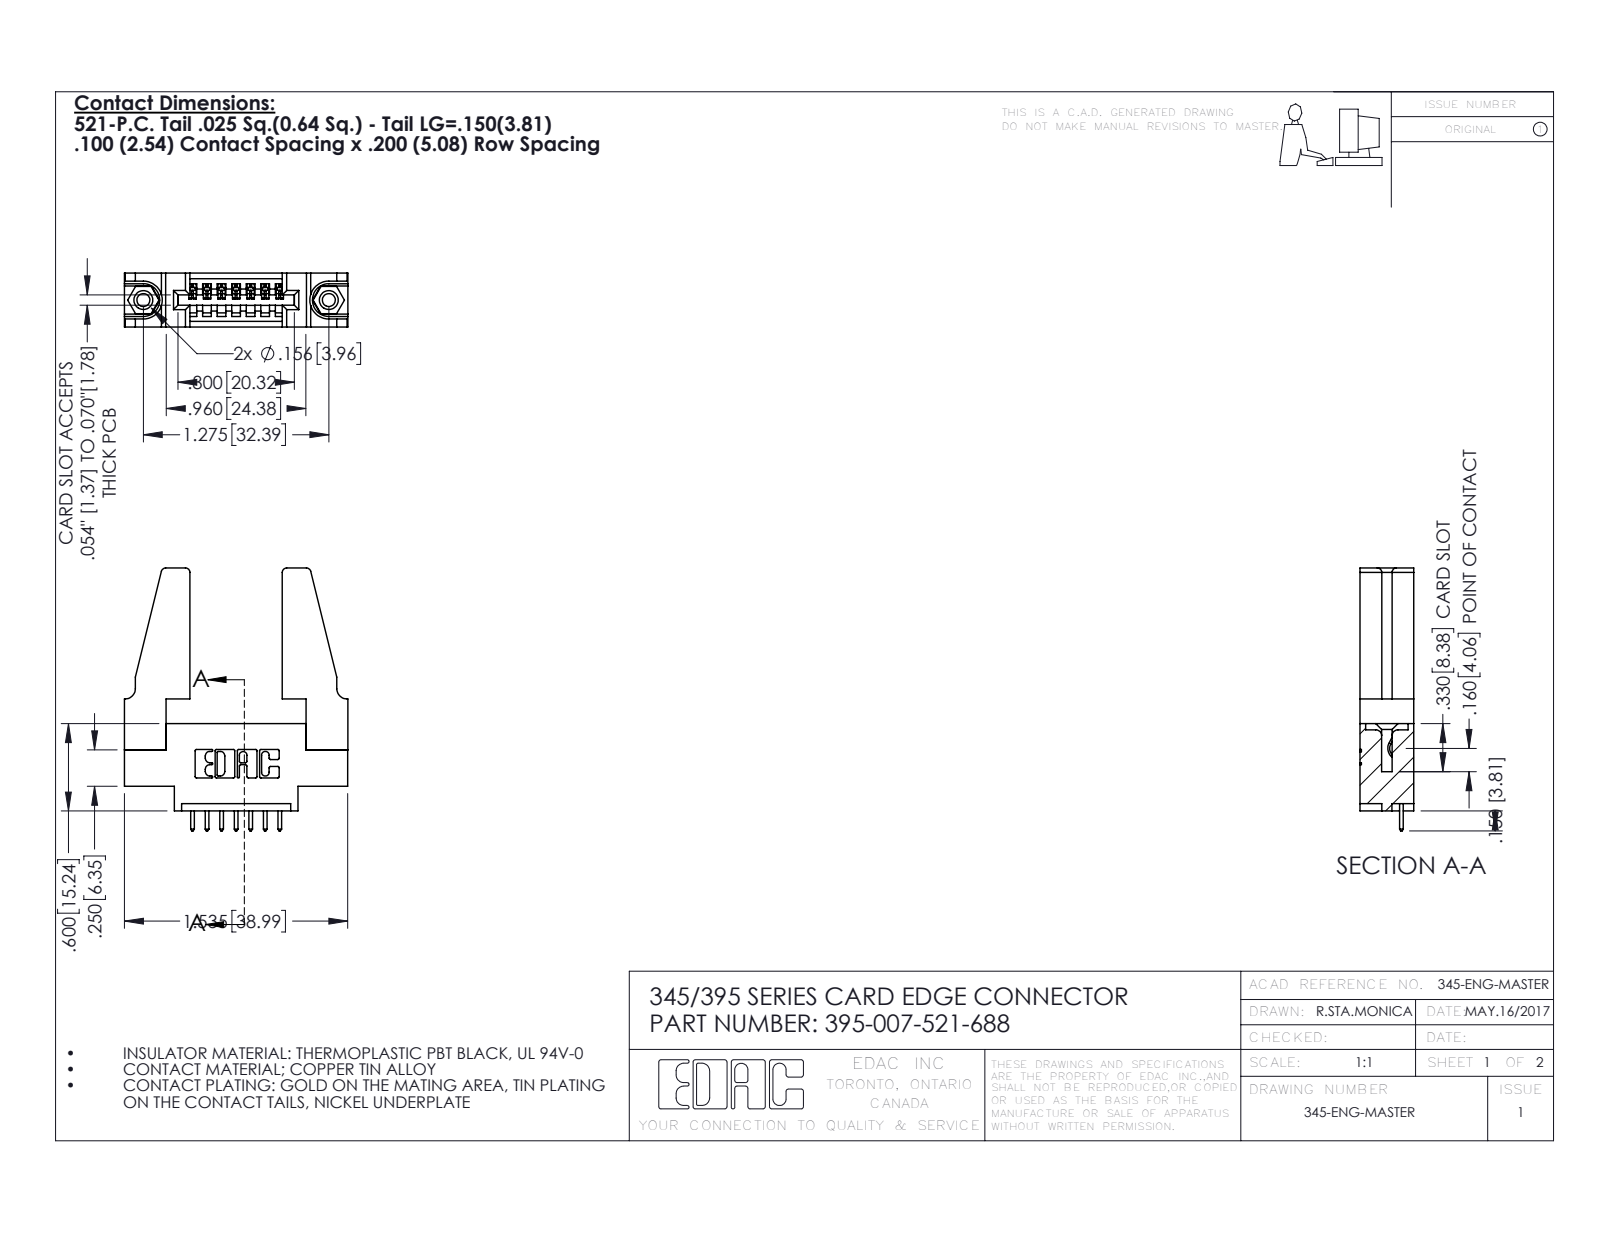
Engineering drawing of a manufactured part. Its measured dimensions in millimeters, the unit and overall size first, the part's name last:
Units: millimetres
Overall size (bounding box): 45.9 × 39 × 9.4
Round holes (diameter × count): ⌀2.3 ×2, ⌀3.2 ×2, ⌀4 ×2, ⌀1.6 ×1
Round bosses / shafts (diameter × count): ⌀3.9 ×2
Partial cylindrical surfaces — rounded edges, fillets, slot ends (radius × count): R0.3 ×22, R0.2 ×14, R0.3 ×14, R0.8 ×8, R0.2 ×6, R0.8 ×6, R0.7 ×3, R0.8 ×2
Main face-to-face distances: 9.4, 1.8, 7.6, 5.1, 3.8, 3.8, 2.5, 6.9, 0.6, 5.6
Hole centre spacings: 6.9, 26.5, 32.4
Volume: 6 540 mm³ · Surface area: 7 071 mm²
Bodies: 12 solids, 660 faces (436 planar, 208 cylindrical, 16 other)
Part name (STEP PRODUCT): 395-007-521-688; 345 Part_0.170 Offset - 0.156 Dia-TH; 345-292-001_345-293-121; 345-220-078_345-220-088 (+1 more)
STEP written by: SolidWorks 2016 (CONFIG_CONTROL_DESIGN)
